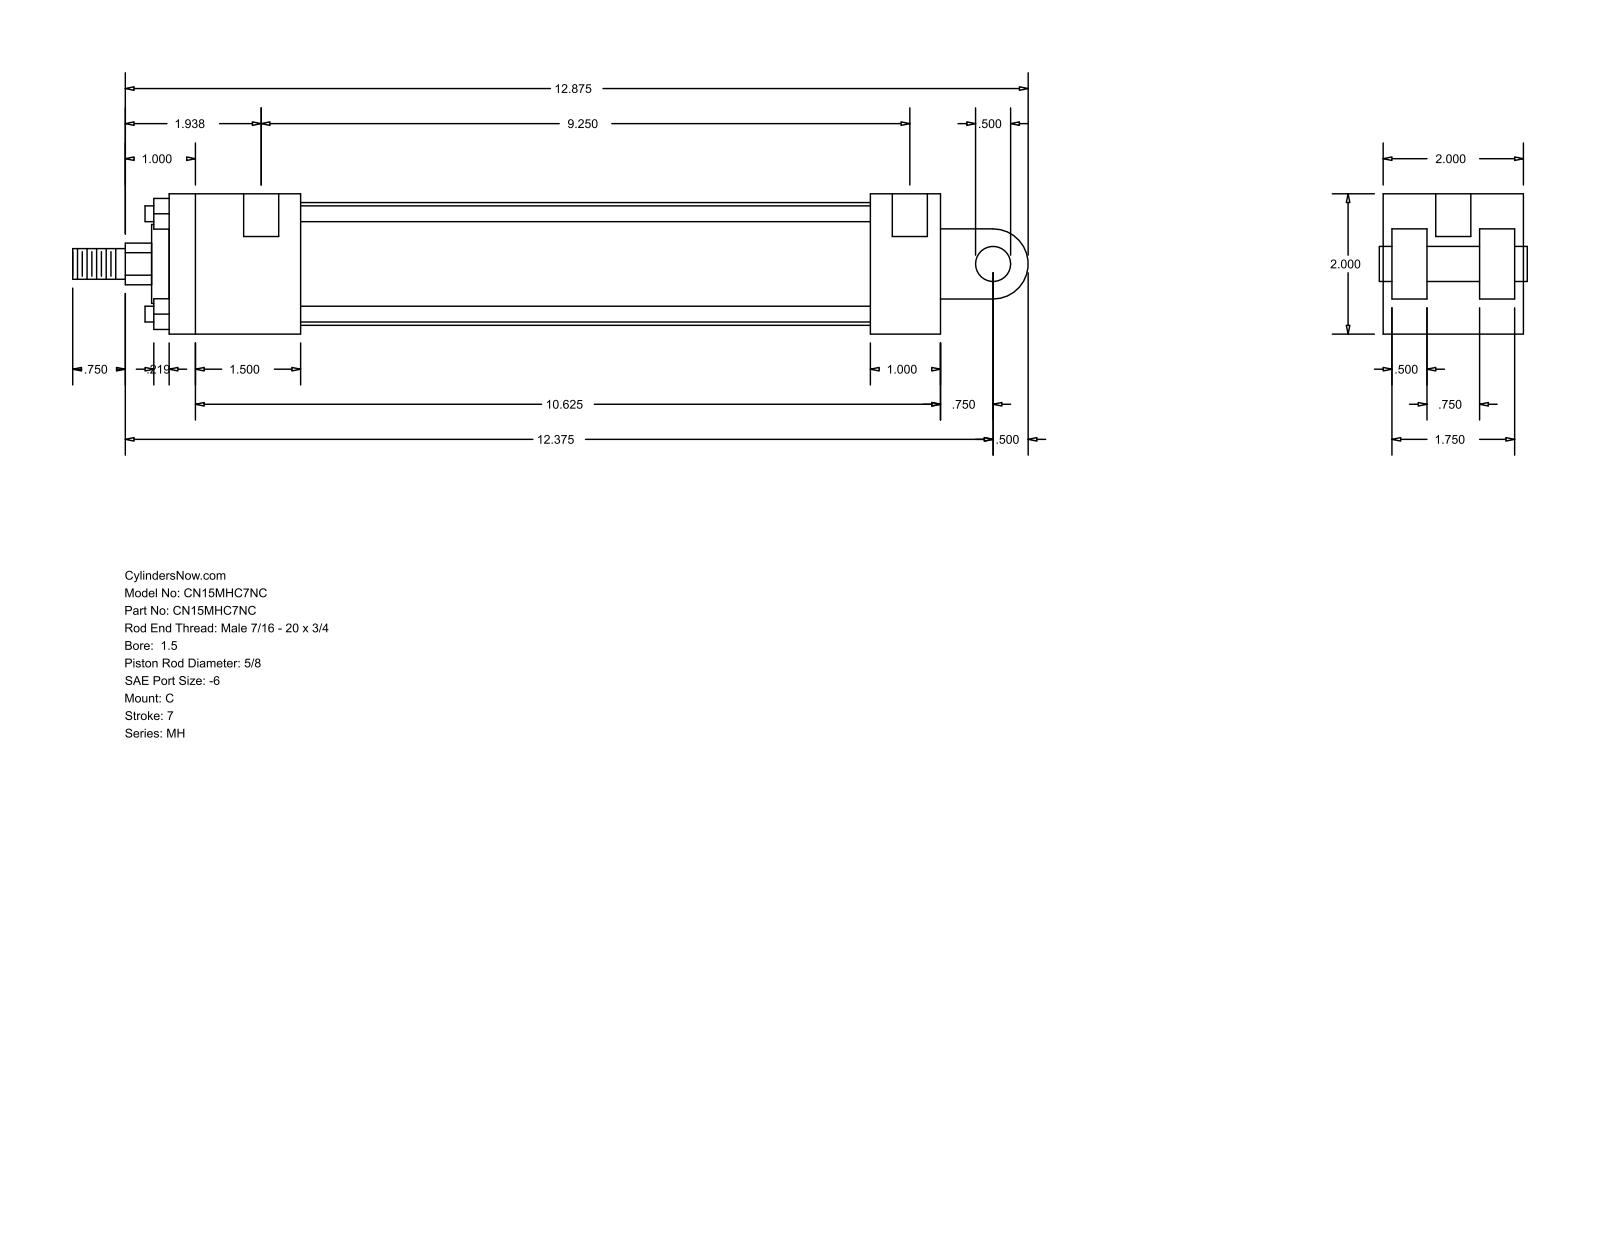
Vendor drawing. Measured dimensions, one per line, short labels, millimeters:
name: MH_C__0150_0.625
written by: GSSL Pune (CONFIG_CONTROL_DESIGN)
unit: mm
bodies: 0 solids, 99 faces (70 planar, 29 cylindrical, 0 other)
size: 346.07 × 50.8 × 50.8
holes: 4× ⌀5.56, 2× ⌀12.7
bosses: 4× ⌀5.71, 1× ⌀44.45, 1× ⌀28.57, 1× ⌀15.88, 1× ⌀12.7, 1× ⌀11.11
rounds: 1× R7.54, 1× R12.7
face distances: 50.8, 12.7, 279.39, 34.93, 3.17, 15.87, 47.63, 31.76, 38.1, 47.62
hole spacings: 238.12, 3.17, 234.95
